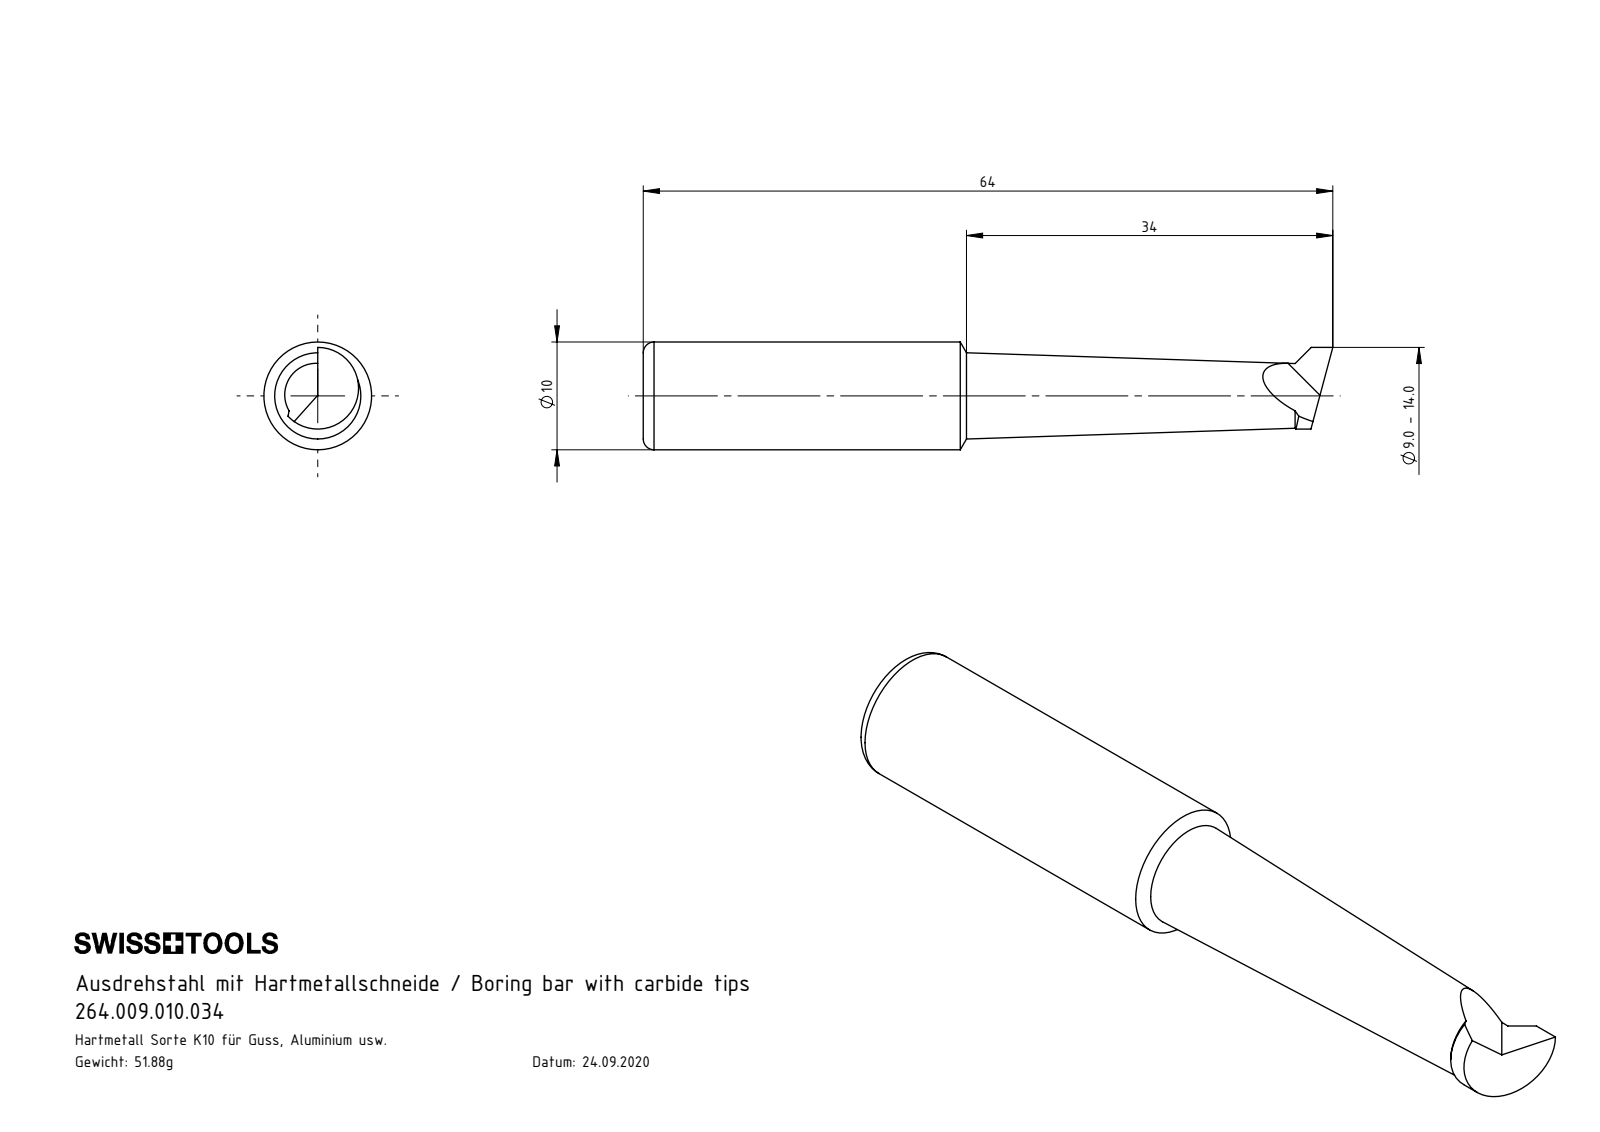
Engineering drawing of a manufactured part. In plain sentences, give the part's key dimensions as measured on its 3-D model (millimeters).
The part is named "U10.B09.001.034". Its 3-D file was written by "SolidWorks 2017 (AUTOMOTIVE_DESIGN)". It is 1 solid with 10 faces: 4 planar, 2 cylindrical and 4 other. Overall it measures 64 by 10 by 10 millimeters. Its volume is 3 578 cubic millimeters and its surface area 1 776 square millimeters. Round bosses or shafts: 1 of diameter 10. Partial cylindrical surfaces (rounded edges, fillets, slot ends): 1 of radius 3.79.
